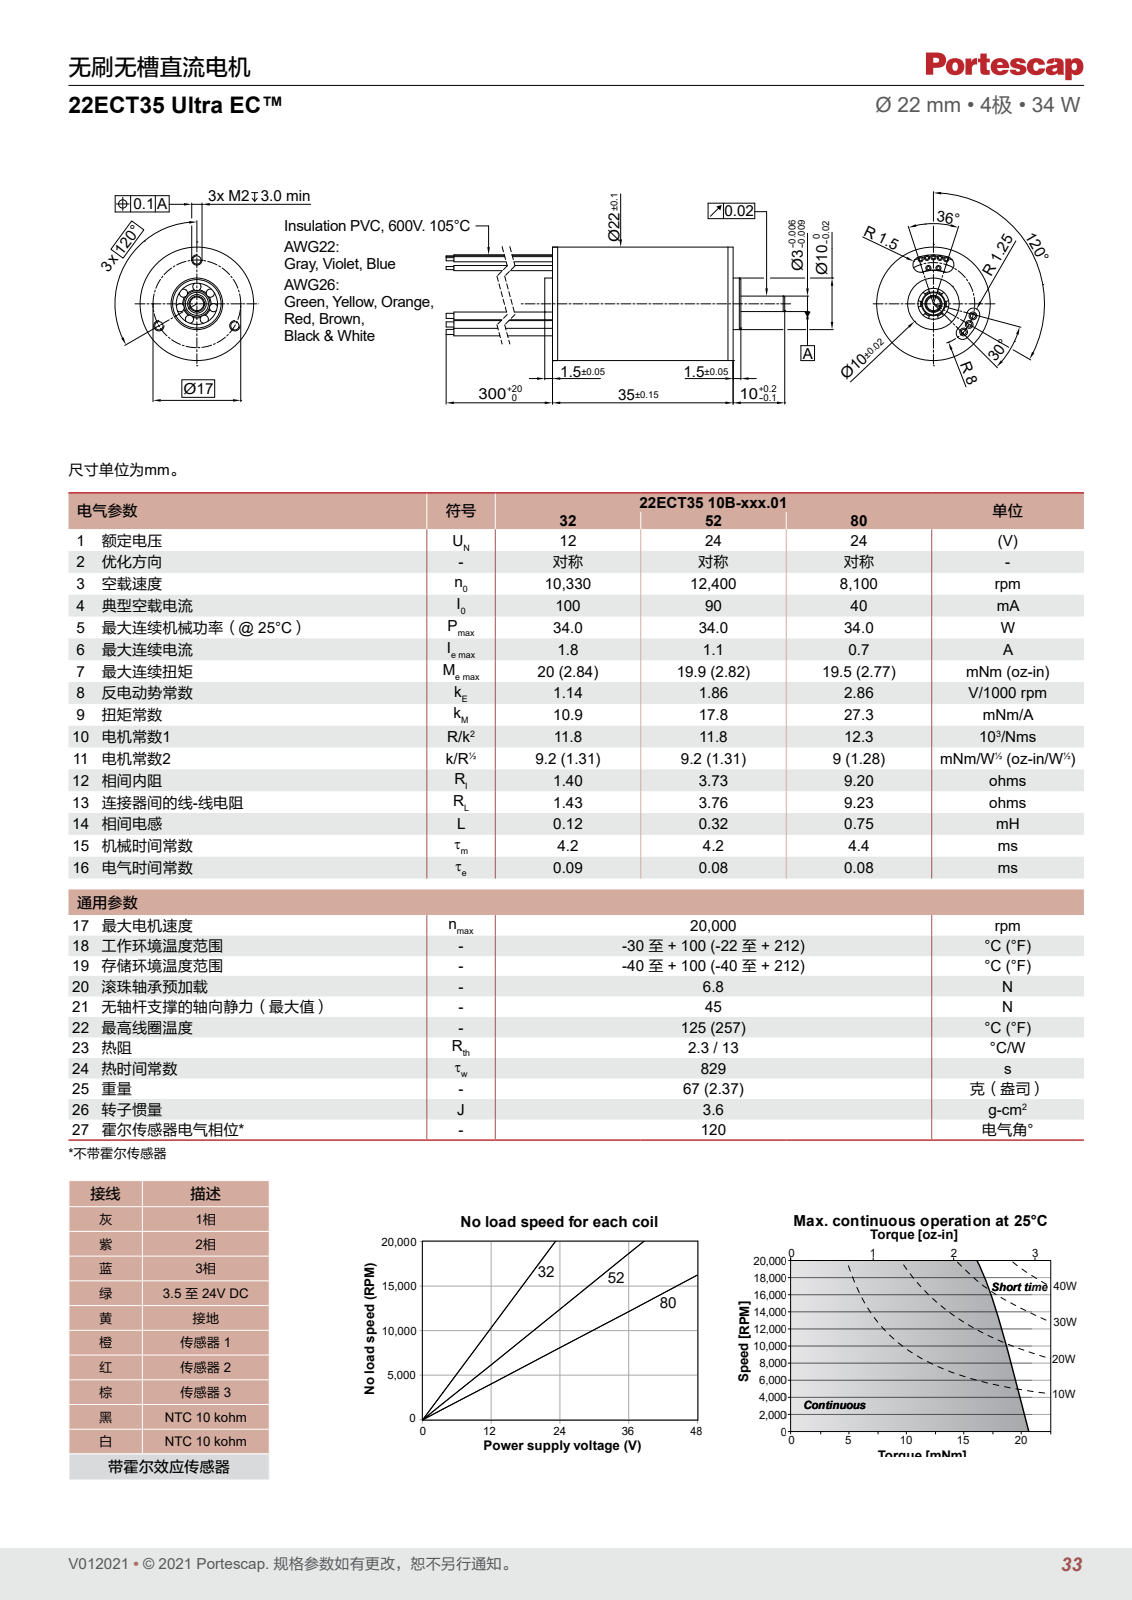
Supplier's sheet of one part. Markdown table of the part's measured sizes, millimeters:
| quantity | value |
| --- | --- |
| part name | 22ECT_35 |
| STEP written by | SolidWorks 2018 (AUTOMOTIVE_DESIGN) |
| units | millimeters |
| bodies | 15 solids, 113 faces (36 planar, 47 cylindrical, 30 other) |
| overall size | 345 × 22 × 22 |
| volume | 16 606 mm³ |
| surface area | 20 563 mm² |
| round holes (diameter × count) | 1.6 × 3, 6 × 1, 8 × 1 |
| round bosses / shafts (diameter × count) | 0.6 × 10, 1 × 7, 1.5 × 3, 22 × 1, 21 × 1, 10 × 1, 3 × 1 |
| partial cylindrical surfaces (radius × count) | 1.25 × 2, 1.5 × 2, 6.5 × 1, 6.75 × 1, 9.25 × 1, 9.5 × 1 |
| main face-to-face distances | 4.85, 30.15, 35, 1, 35.5, 1.5, 34.3, 4.15, 0.7, 34 |
| hole center spacings | 8.5, 14.72 |
